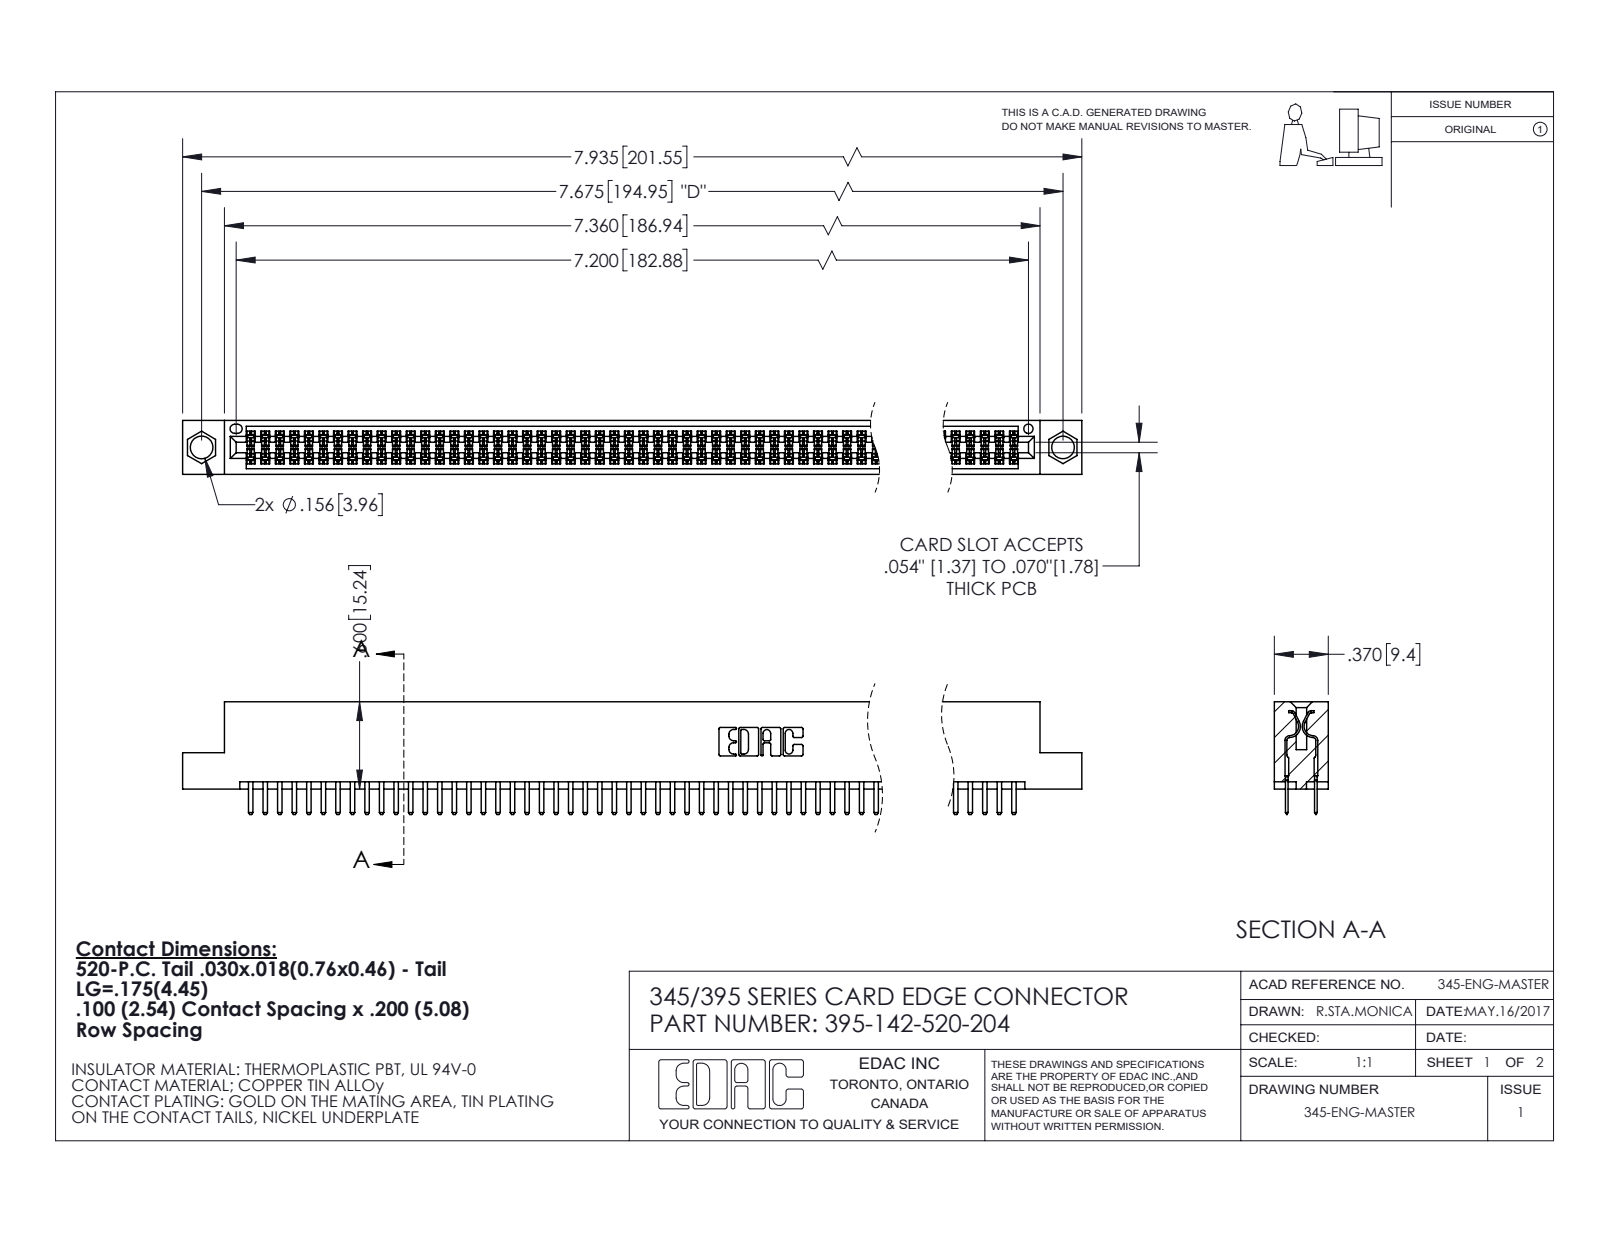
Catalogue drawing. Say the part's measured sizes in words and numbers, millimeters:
The part is named "345 Part_Flush Mounting Lugs - 0.156 Dia-TI; 345-292-001_345-293-120; 395-142-520-204". Its 3-D file was written by "SolidWorks 2020 (CONFIG_CONTROL_DESIGN)". It is 143 solids with 7808 faces: 5064 planar, 2744 cylindrical and 0 other. Overall it measures 201.5 by 19.7 by 9.4 millimeters. Its volume is 19 680 cubic millimeters and its surface area 29 370 square millimeters. Round holes: 2 of diameter 4, 1 of diameter 1.6. Partial cylindrical surfaces (rounded edges, fillets, slot ends): 213 of radius 0.2, 146 of radius 0.3, 22 of radius 0.3, 6 of radius 0.2, 6 of radius 0.8, 3 of radius 0.7, 2 of radius 0.4, 2 of radius 0.5. The main face-to-face distances are 7.6, 1.8, 5.1, 9.4, 2.5, 6.9, 0.6, 5.7, 0.6, 1.8. The hole center spacings are 6.9, 189, 194.9.
